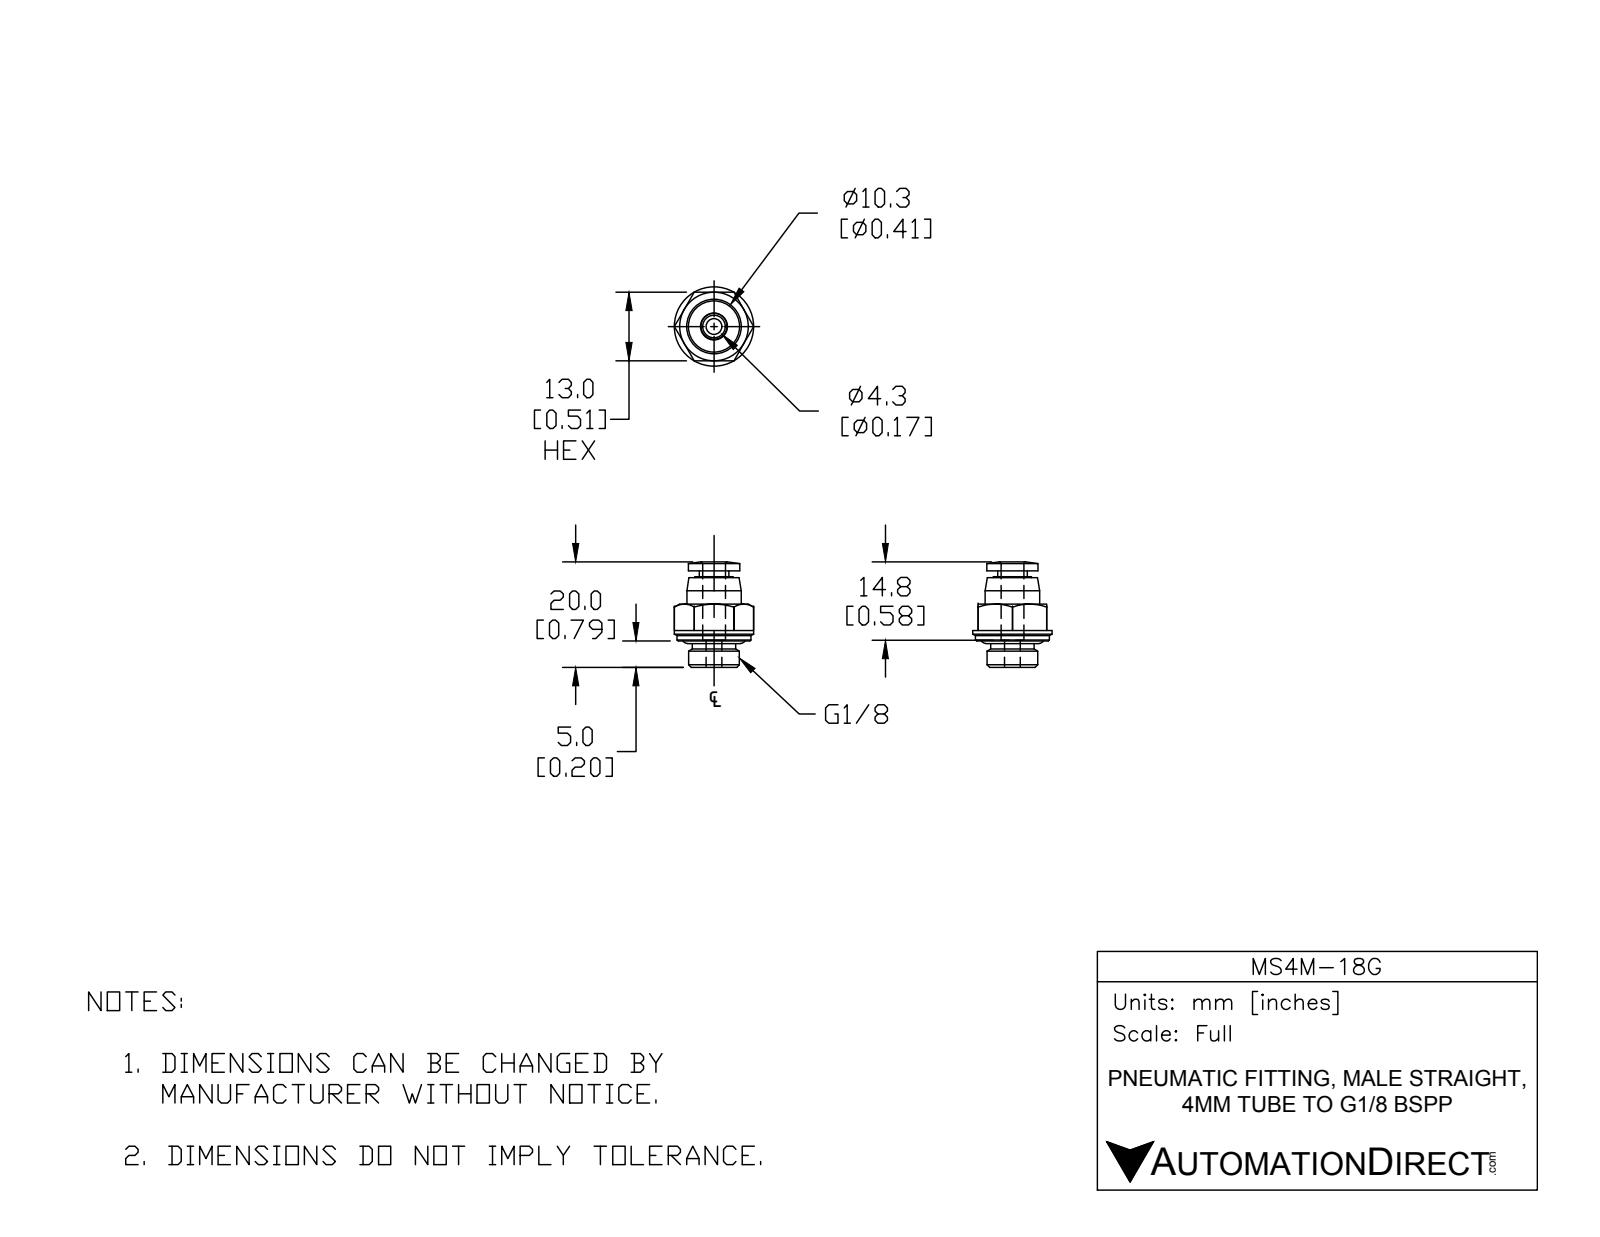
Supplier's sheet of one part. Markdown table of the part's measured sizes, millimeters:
| quantity | value |
| --- | --- |
| part name | MS4M-18G |
| STEP written by | SolidWorks 2015 (AUTOMOTIVE_DESIGN) |
| units | millimeters |
| bodies | 2 solids, 69 faces (21 planar, 22 cylindrical, 26 other) |
| overall size | 19.9 × 15 × 15 |
| volume | 1 690 mm³ |
| surface area | 1 613 mm² |
| round holes (diameter × count) | 3 × 1, 4.3 × 1 |
| round bosses / shafts (diameter × count) | 15 × 1, 14 × 1, 10.3 × 1, 9.7 × 1, 9.6 × 1, 8.2 × 1, 7.2 × 1, 5.6 × 1 |
| main face-to-face distances | 13, 5, 12, 11.9, 18.3, 6.2, 7, 6.4, 5.6, 1.2 |
